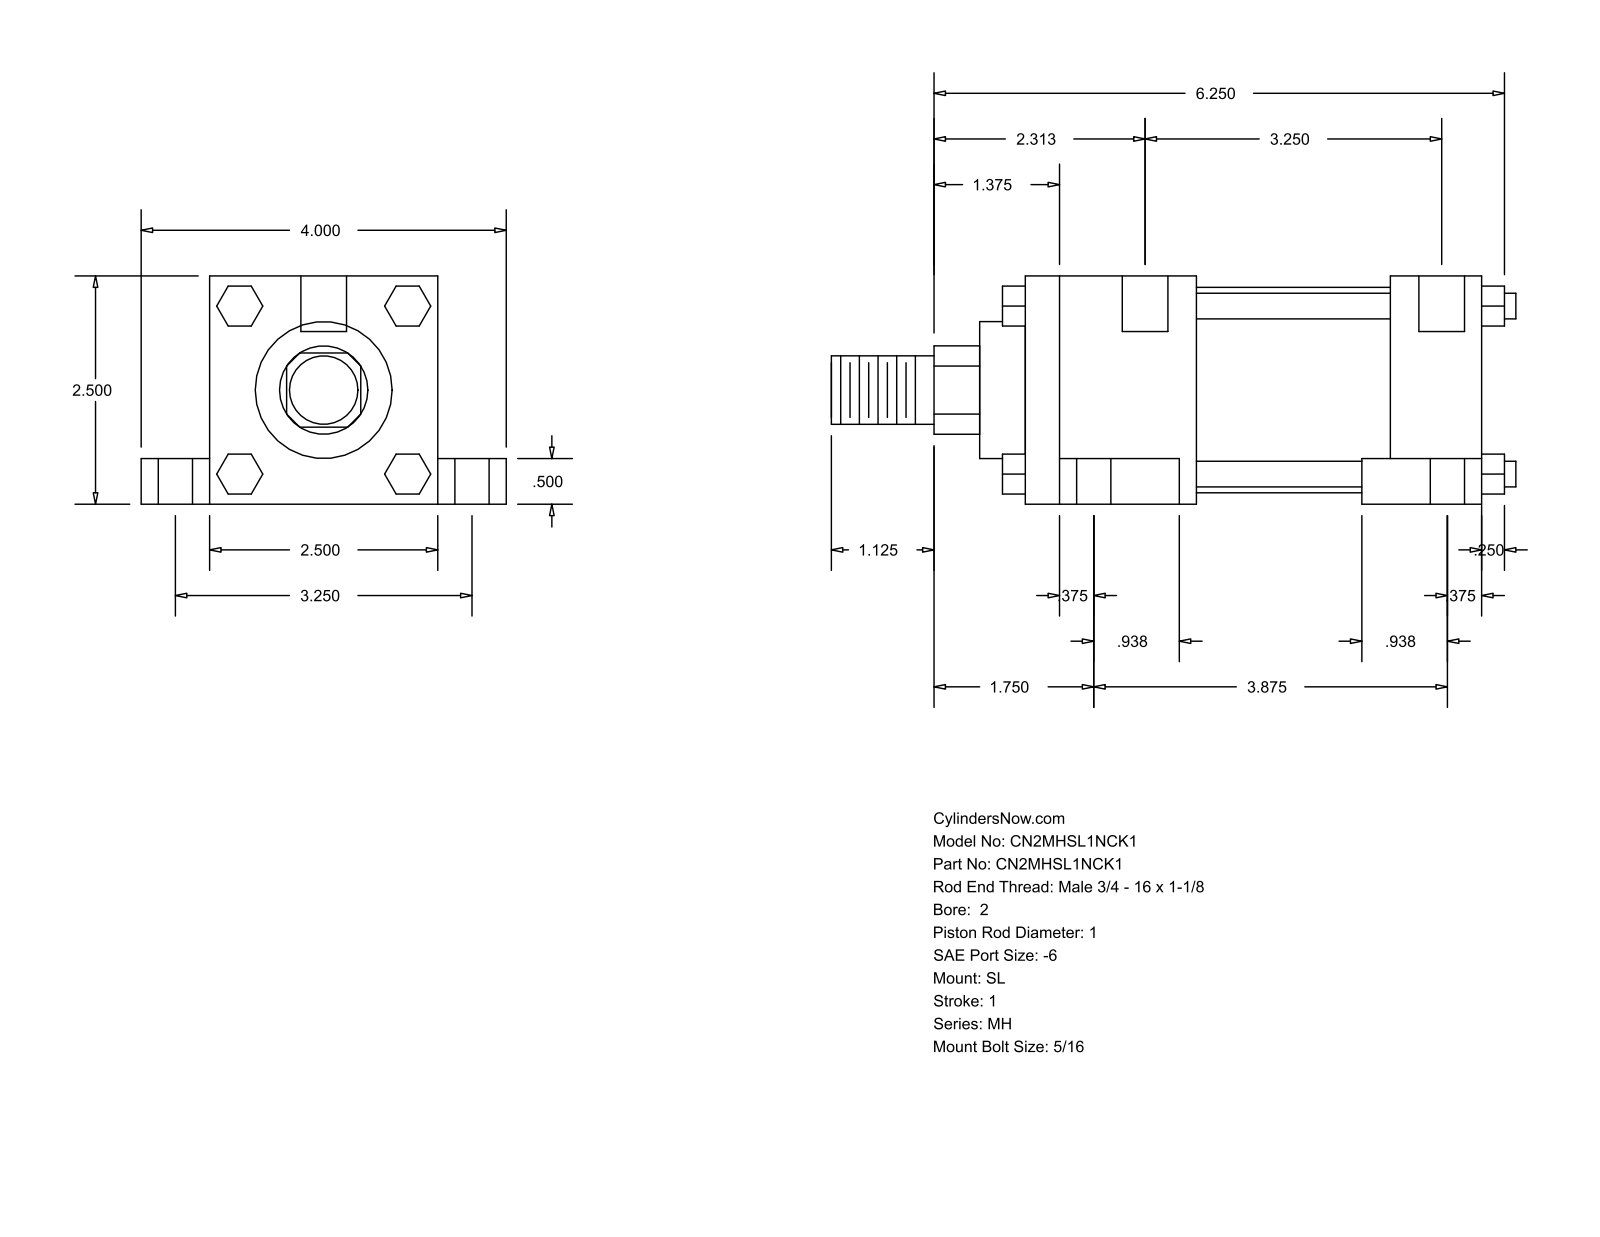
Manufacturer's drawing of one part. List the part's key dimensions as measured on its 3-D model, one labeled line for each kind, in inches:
Part name (STEP PRODUCT): MH_SL__0200_1
STEP written by: GSSL Pune (CONFIG_CONTROL_DESIGN)
Units: inches
Bodies: 0 solids, 148 faces (112 planar, 36 cylindrical, 0 other)
Overall size (bounding box): 7.5 × 4 × 2.5
Round holes (diameter × count): ⌀0.219 ×4, ⌀0.375 ×4, ⌀0.625 ×4, ⌀0.5 ×2
Round bosses / shafts (diameter × count): ⌀0.281 ×4, ⌀2.25 ×1, ⌀1.5 ×1, ⌀1 ×1, ⌀0.75 ×1
Partial cylindrical surfaces — rounded edges, fillets, slot ends (radius × count): R0.484 ×1
Main face-to-face distances: 2.5, 5, 0.5, 4, 2, 0.75, 3.25, 2.125, 1, 1.875
Hole centre spacings: 1.626, 1.668, 1.719, 3.25, 3.562, 3.69, 3.859, 3.875
